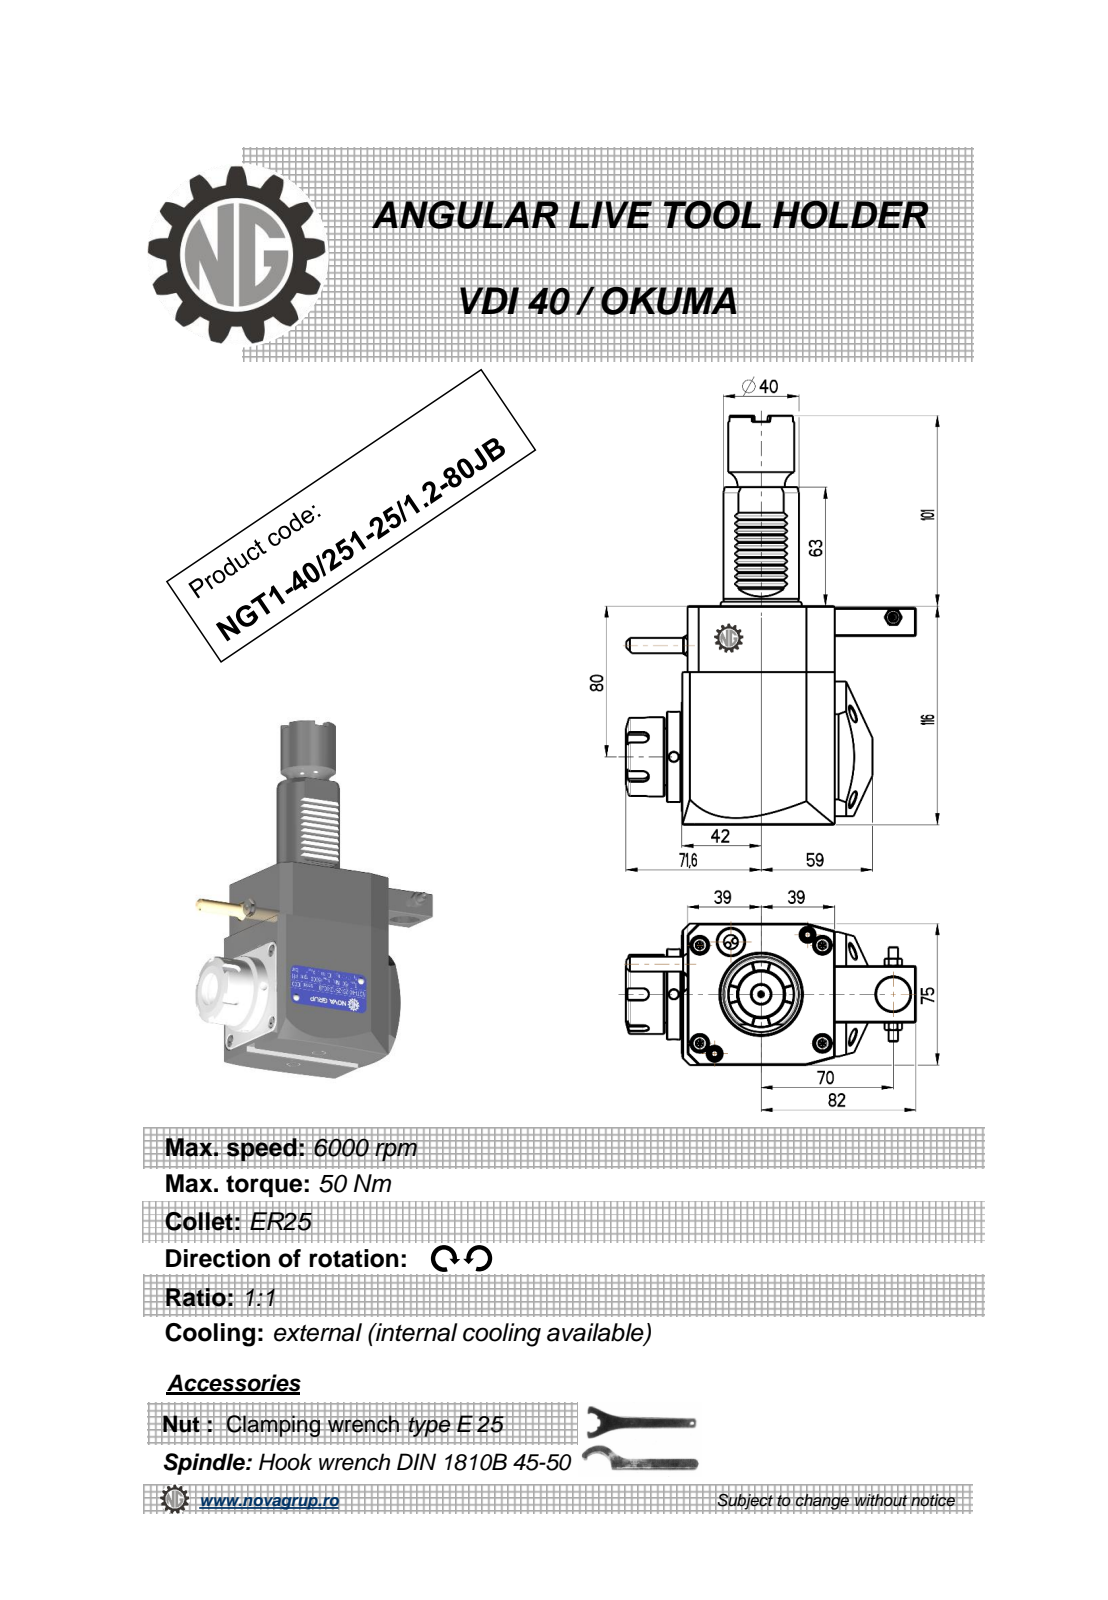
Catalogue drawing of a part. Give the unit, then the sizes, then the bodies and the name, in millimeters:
Units: millimetres
Overall size (bounding box): 217 × 153.6 × 76.6
Round holes (diameter × count): ⌀5 ×3, ⌀3 ×1, ⌀4.2 ×1, ⌀9.5 ×1, ⌀18 ×1, ⌀20.3 ×1, ⌀25 ×1
Round bosses / shafts (diameter × count): ⌀48 ×1, ⌀42 ×1, ⌀40 ×1, ⌀37.5 ×1, ⌀35 ×1, ⌀33 ×1, ⌀10 ×1, ⌀8.96 ×1
Partial cylindrical surfaces — rounded edges, fillets, slot ends (radius × count): R0.26 ×12, R0.3 ×10, R0.2 ×6, R3 ×5, R0.5 ×1, R40 ×1
Main face-to-face distances: 75, 116, 81, 3, 78, 2.8, 80.8, 1, 96, 112
Hole centre spacings: 20.93, 46.25, 61.13, 70, 72.5, 116.25, 137.8
Volume: 898 348 mm³ · Surface area: 75 760 mm²
Bodies: 1 solid, 489 faces (210 planar, 92 cylindrical, 187 other)
Part name (STEP PRODUCT): NGT1_40_251_25_1_2_80JB
STEP written by: PRO/ENGINEER BY PARAMETRIC TECHNOLOGY CORPORATION, 2010280 (CONFIG_CONTROL_DESIGN)
